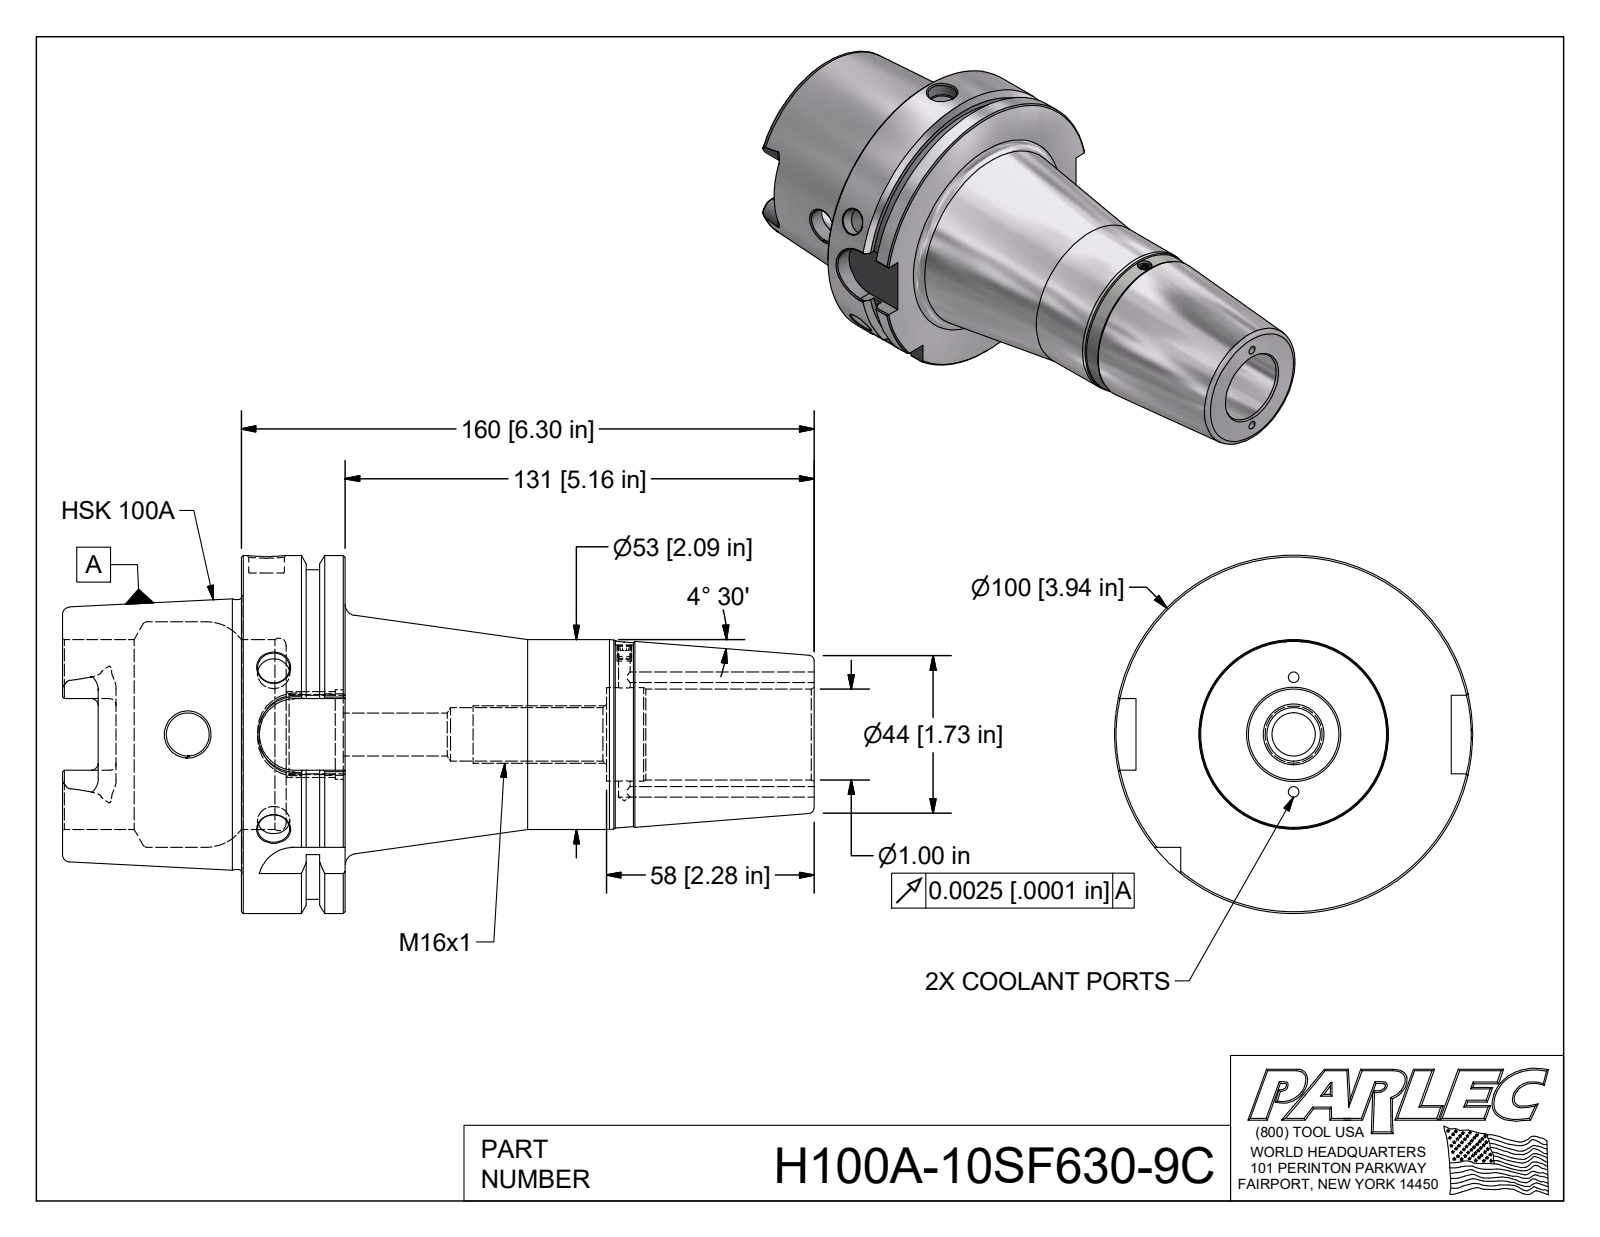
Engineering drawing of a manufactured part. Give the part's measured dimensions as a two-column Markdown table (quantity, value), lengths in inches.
| quantity | value |
| --- | --- |
| STEP written by | Autodesk Inventor 2018 (AUTOMOTIVE_DESIGN) |
| units | inches |
| bodies | 1 solid, 154 faces (49 planar, 42 cylindrical, 63 other) |
| overall size | 8.268 × 3.937 × 3.937 |
| volume | 31.39 in³ |
| surface area | 122 in² |
| round holes (diameter × count) | 0.118 × 2, 0.354 × 2, 0.472 × 2, 0.128 × 1, 0.197 × 1, 0.394 × 1, 0.587 × 1, 0.881 × 1, 0.985 × 1, 0.999 × 1, 1.029 × 1, 2.087 × 1 |
| round bosses / shafts (diameter × count) | 3.937 × 1, 3.622 × 1, 2.967 × 1 |
| partial cylindrical surfaces (radius × count) | 0.079 × 6, 0.192 × 4, 0.394 × 4 |
| main face-to-face distances | 1.142, 0.492, 0.65, 1.969, 2.461, 3.11, 8.268, 6.299, 5.807, 5.157 |
| hole center spacings | 0.63, 1.26, 3.937 |
